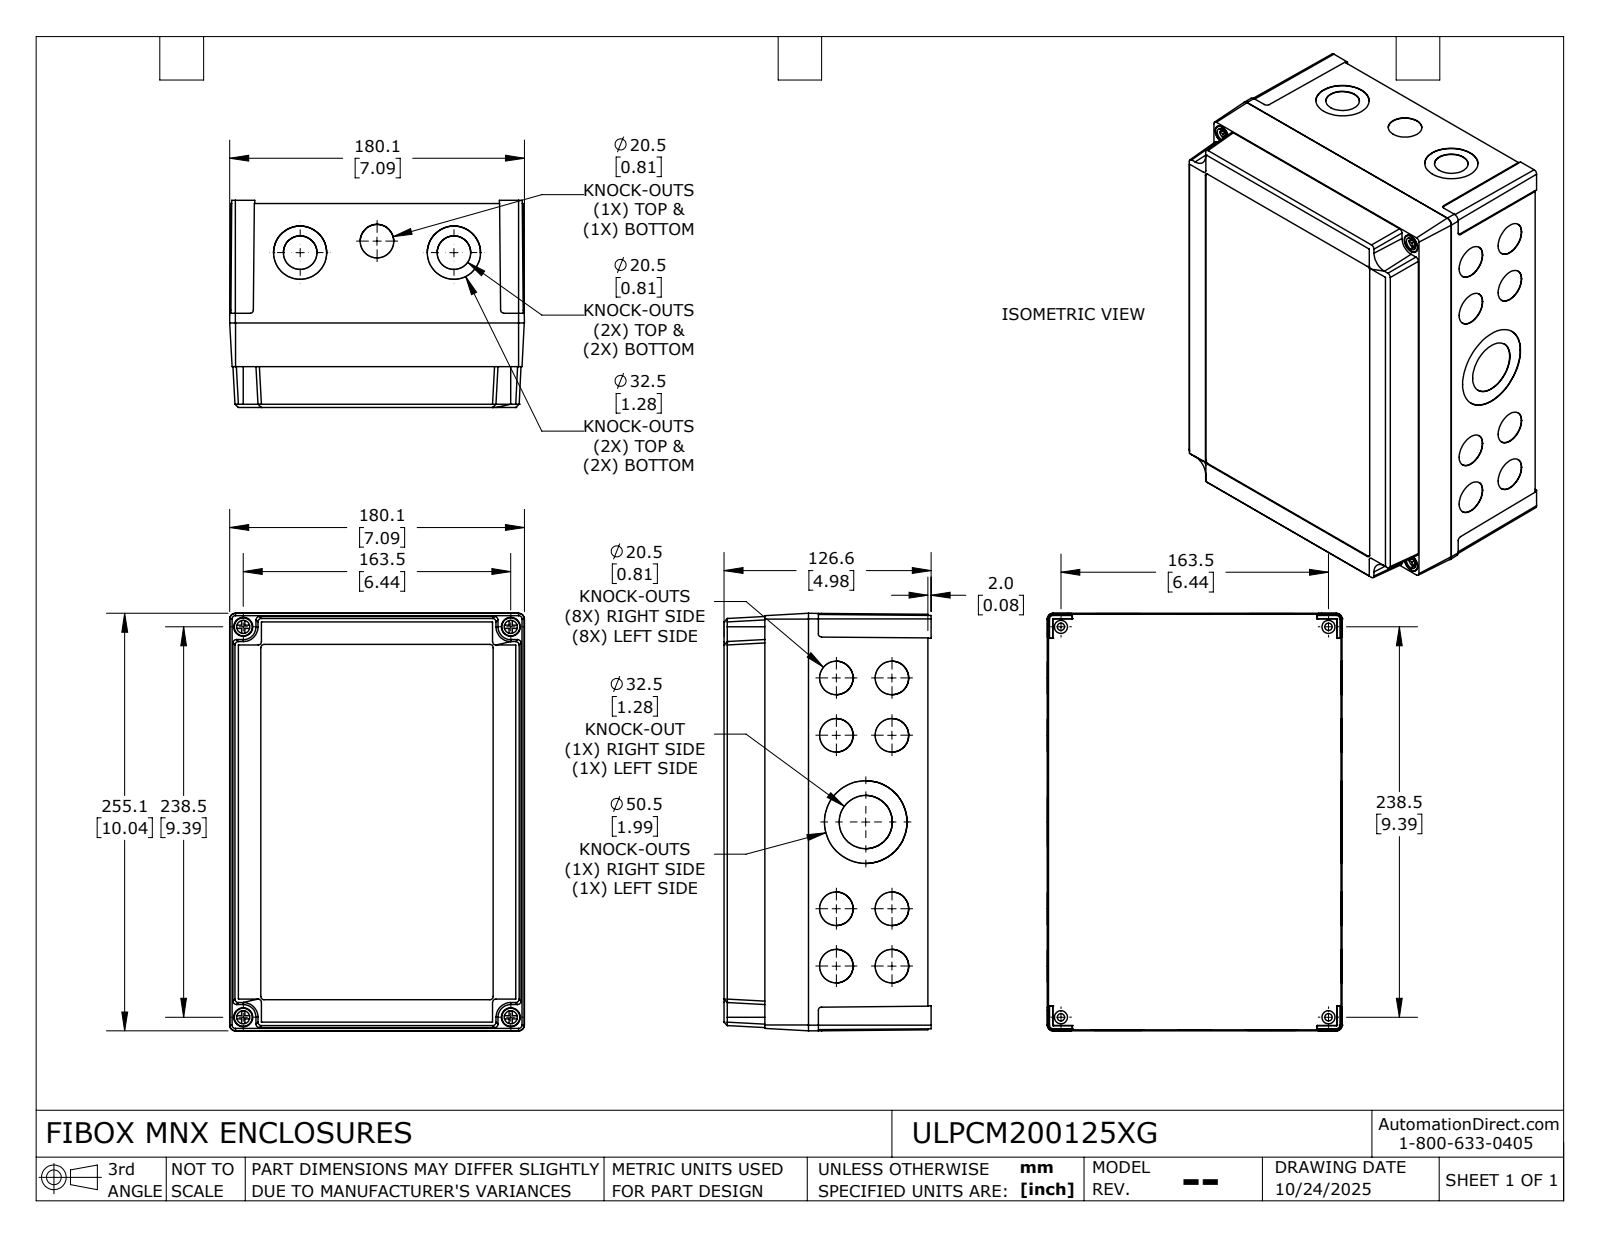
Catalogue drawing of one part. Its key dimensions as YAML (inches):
part_name: "ULPCM200125XG_Default"
step_written_by: "SolidWorks 2024 (CONFIG_CONTROL_DESIGN)"
units: inches
bodies: {solids: 6, faces: 767, planar: 425, cylindrical: 292, other: 50}
overall_size: [10.043, 7.091, 4.984]
volume: 37.21
surface_area: 628
round_holes:
  - {diameter: 0.807, count: 22}
  - {diameter: 0.126, count: 20}
  - {diameter: 0.157, count: 20}
  - {diameter: 1.28, count: 6}
  - {diameter: 0.177, count: 4}
  - {diameter: 0.315, count: 4}
  - {diameter: 0.457, count: 4}
  - {diameter: 1.988, count: 2}
round_bosses_or_shafts:
  - {diameter: 0.315, count: 16}
  - {diameter: 0.098, count: 8}
  - {diameter: 0.433, count: 4}
  - {diameter: 0.283, count: 4}
  - {diameter: 0.276, count: 4}
partial_cylinders:
  - {radius: 0.079, count: 8}
  - {radius: 0.083, count: 8}
  - {radius: 0.112, count: 6}
  - {radius: 0.042, count: 4}
  - {radius: 0.197, count: 4}
  - {radius: 0.046, count: 2}
face_to_face_distances: [0.165, 4.803, 0.118, 4.685, 4.886, 4.768, 0.083, 0.077, 0.055, 0.022]
hole_center_spacings: [1.378, 1.339, 1.921, 1.939, 5.046, 5.551, 5.71, 4.921]
